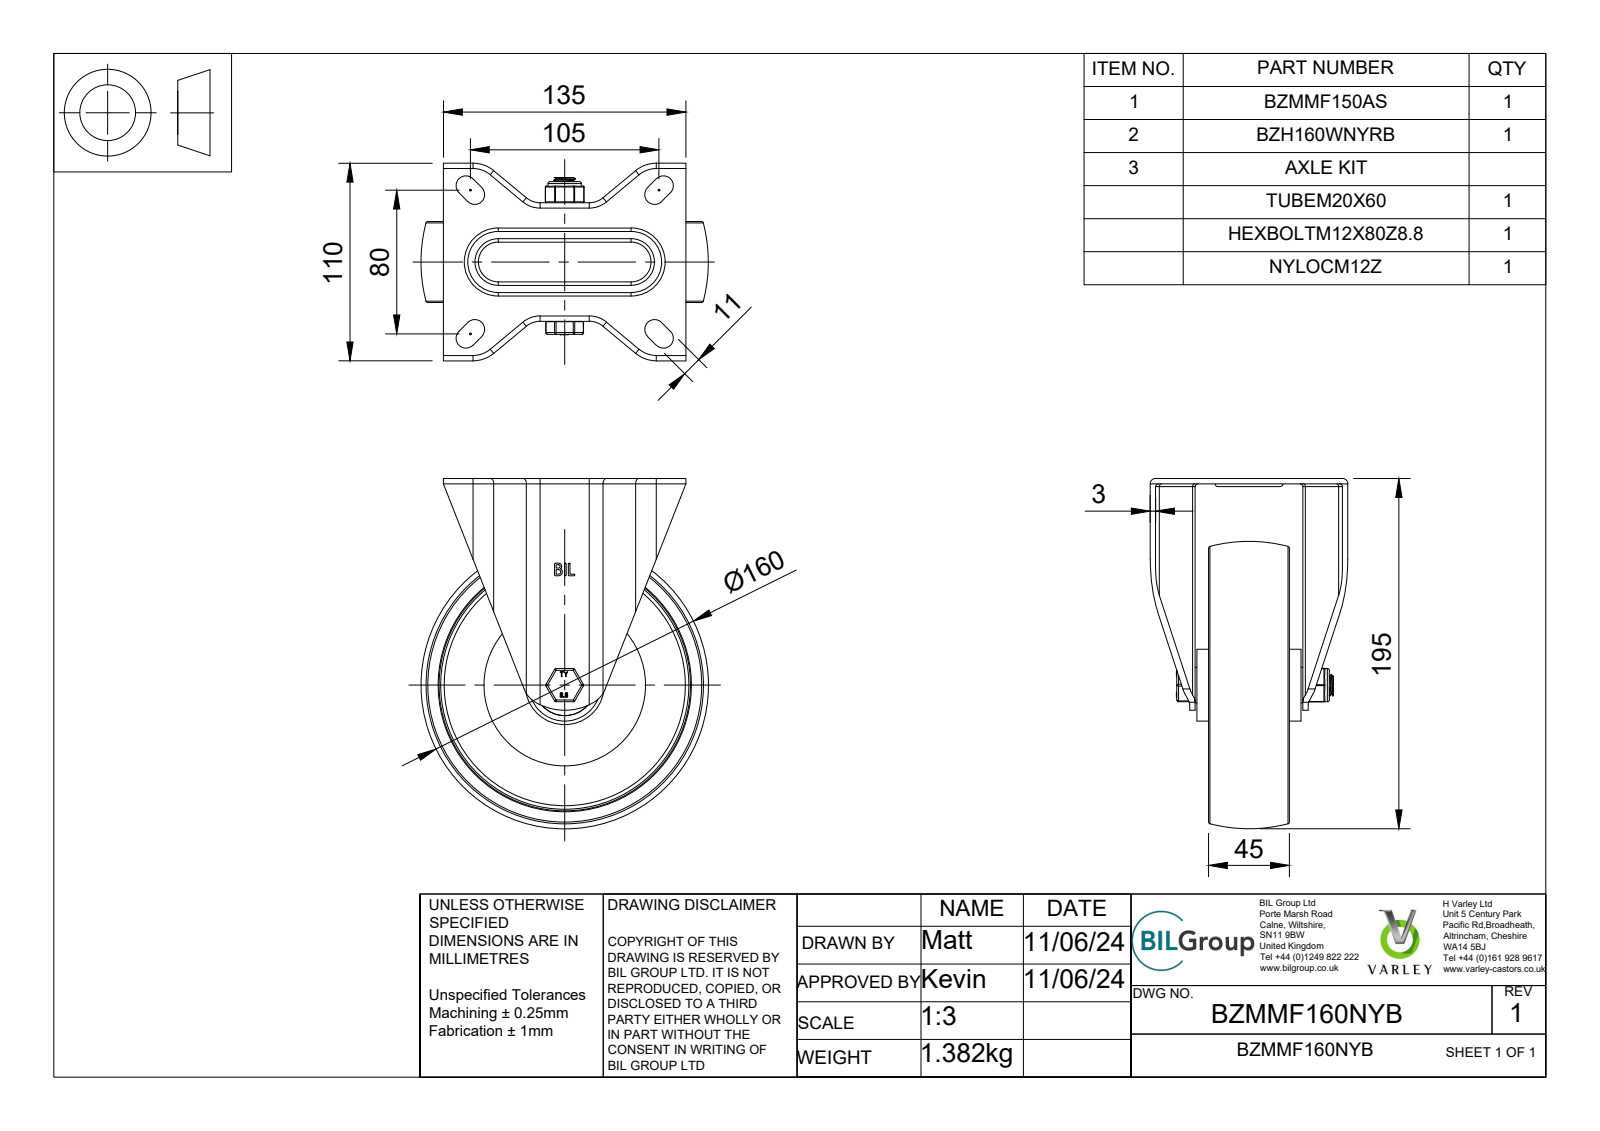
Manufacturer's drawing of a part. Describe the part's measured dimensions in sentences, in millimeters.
The part is named "BZMMF160NYB v3; BZMMF150AS v1; BZMMF150AS; ZINC PLATED, PRESSED STEEL BRACKET (+8 more)". Its 3-D file was written by "Autodesk Translation Framework v13.14.0.145 (AUTOMOTIVE_DESIGN)". It is 16 solids with 474 faces: 197 planar, 171 cylindrical and 106 other. Overall it measures 195 by 160 by 110 millimeters. Its volume is 530 931 cubic millimeters and its surface area 192 811 square millimeters. Round holes: 1 of diameter 12, 1 of diameter 12.25, 1 of diameter 12.5, 1 of diameter 14, 1 of diameter 20, 1 of diameter 20.2. Round bosses or shafts: 8 of diameter 7.5, 1 of diameter 40, 1 of diameter 34, 1 of diameter 19.9, 1 of diameter 18.5, 1 of diameter 18, 1 of diameter 11.83, 1 of diameter 9.84. Partial cylindrical surfaces (rounded edges, fillets, slot ends): 18 of radius 0.5, 12 of radius 1, 12 of radius 1.5, 8 of radius 3, 8 of radius 5.5, 4 of radius 2, 4 of radius 6, 4 of radius 9. The main face-to-face distances are 3, 25, 24.74, 35, 10, 28, 38, 63, 60, 10.5.
